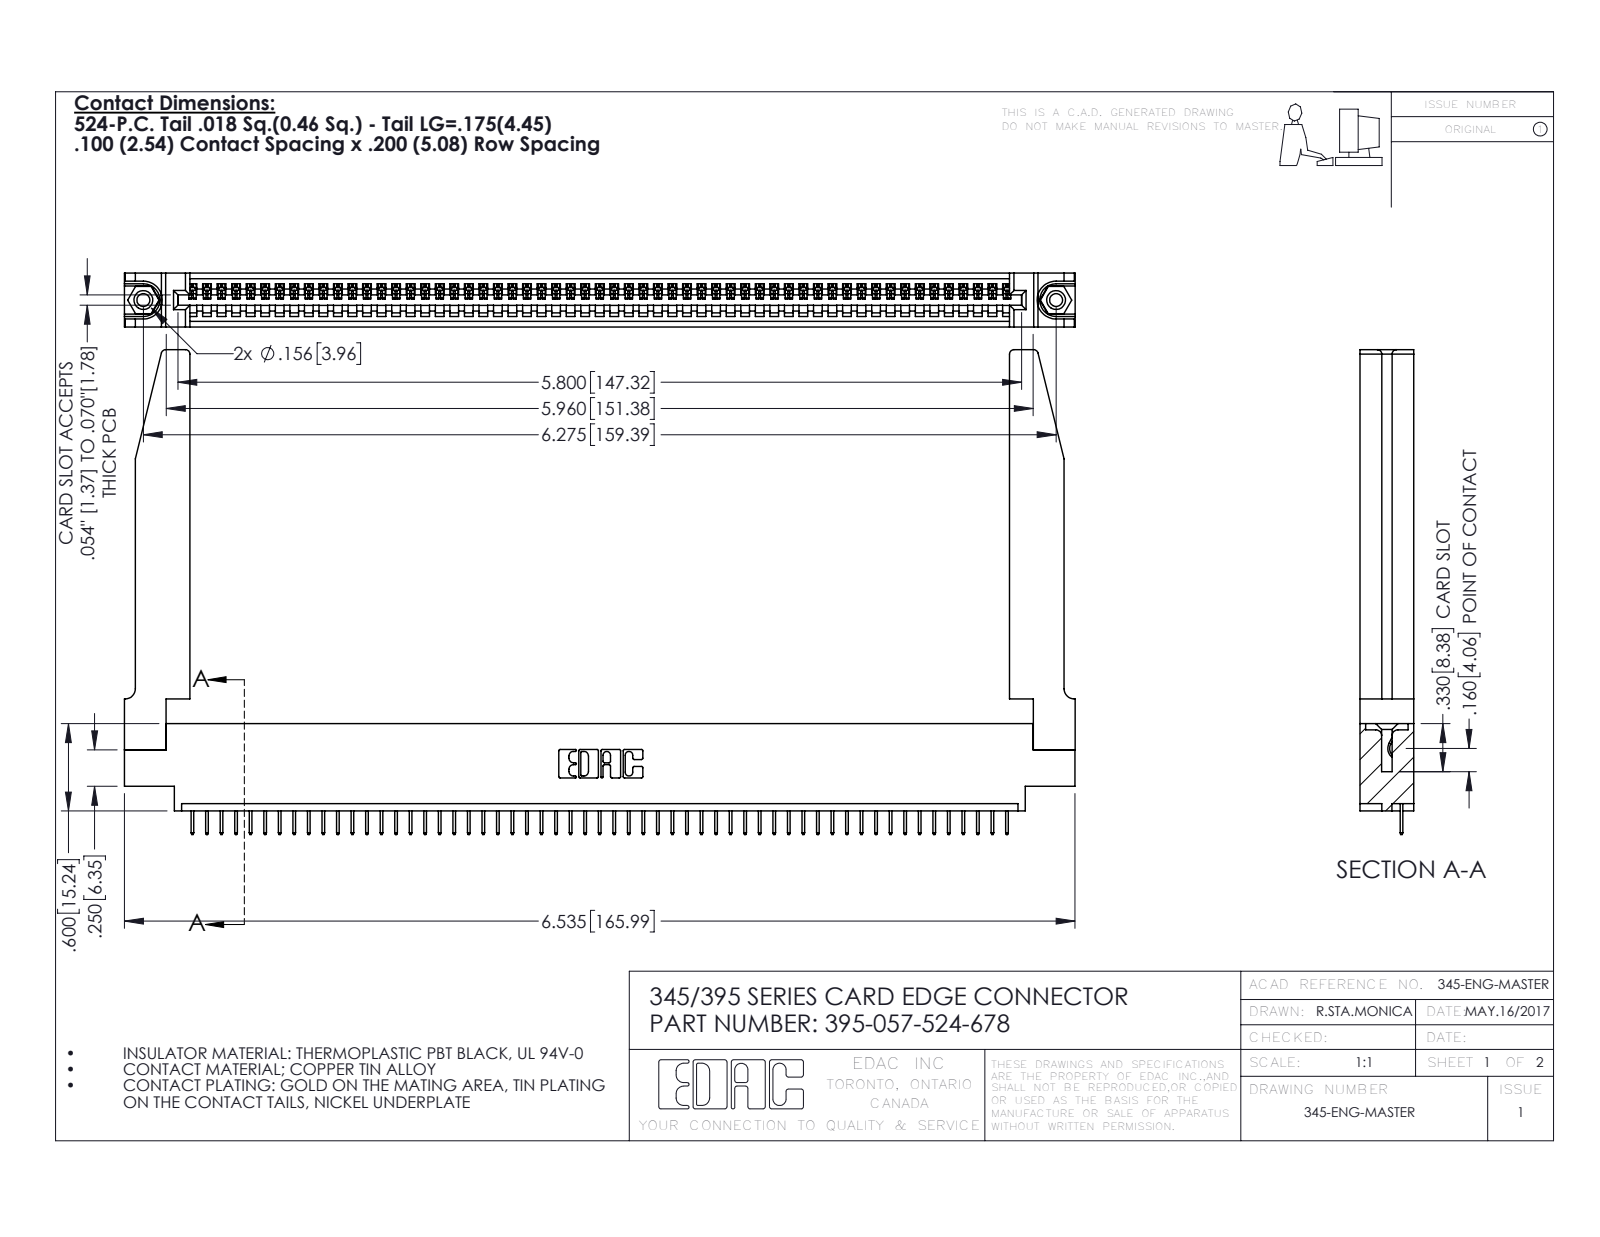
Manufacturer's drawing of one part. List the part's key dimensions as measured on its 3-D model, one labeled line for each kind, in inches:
Part name (STEP PRODUCT): 345-292-001_345-293-124; 345-220-078_345-220-078; 345 Part_0.170 Offset - 0.156 Dia-TH; 345-250-001_345-250-001-102 (+1 more)
STEP written by: SolidWorks 2016 (CONFIG_CONTROL_DESIGN)
Units: inches
Bodies: 62 solids, 3898 faces (2848 planar, 998 cylindrical, 52 other)
Overall size (bounding box): 6.536 × 3.332 × 0.37
Volume: 1.423 in³ · Surface area: 42.04 in²
Round holes (diameter × count): ⌀0.089 ×2, ⌀0.125 ×2, ⌀0.156 ×2, ⌀0.064 ×1
Round bosses / shafts (diameter × count): ⌀0.155 ×2
Partial cylindrical surfaces — rounded edges, fillets, slot ends (radius × count): R0.006 ×114, R0.01 ×22, R0.03 ×8, R0.007 ×6, R0.031 ×6, R0.026 ×3, R0.031 ×2, R0.04 ×2
Main face-to-face distances: 0.37, 0.072, 0.298, 0.098, 0.272, 0.025, 0.2, 0.225, 0.072, 0.148
Hole centre spacings: 0.27, 6.039, 6.275
